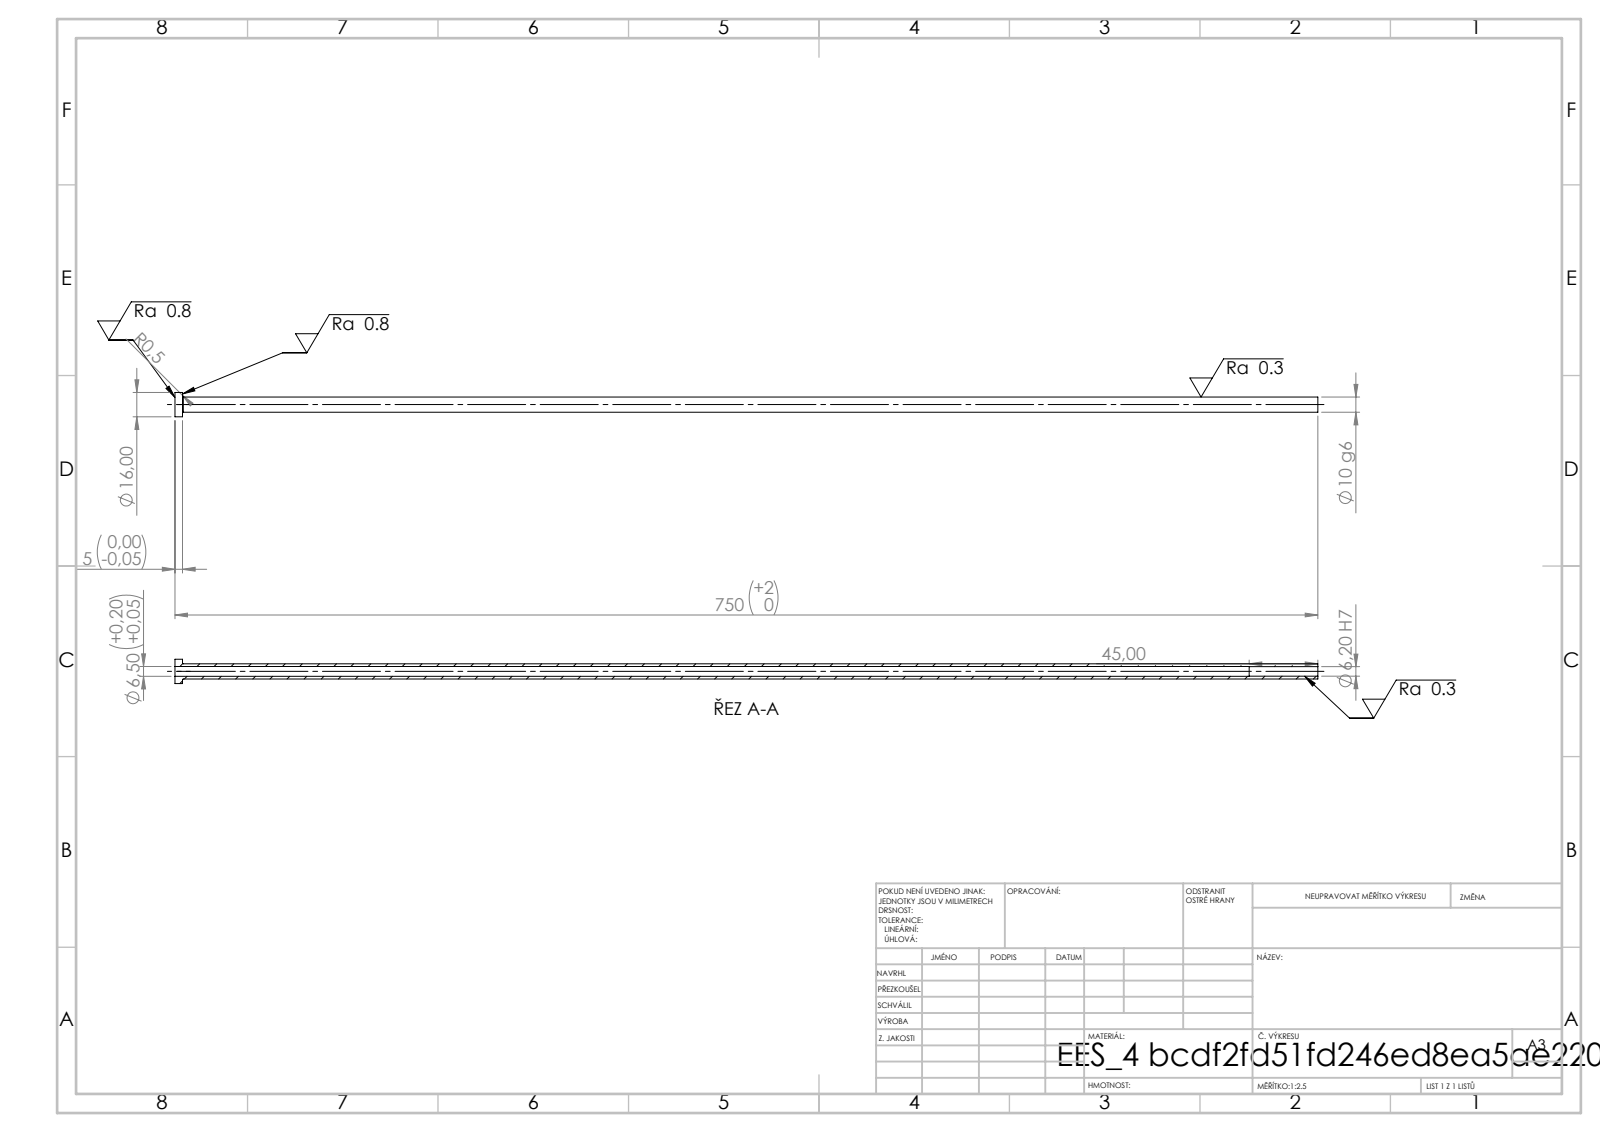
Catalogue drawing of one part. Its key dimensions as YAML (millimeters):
step_written_by: "SolidWorks 2019 (CONFIG_CONTROL_DESIGN)"
units: millimeters
bodies: {solids: 1, faces: 14, planar: 4, cylindrical: 8, other: 2}
overall_size: [750, 16, 16]
volume: 34767
surface_area: 39264
round_holes:
  - {diameter: 6.2, count: 1}
  - {diameter: 6.5, count: 1}
round_bosses_or_shafts:
  - {diameter: 16, count: 1}
  - {diameter: 10, count: 1}
face_to_face_distances: [5, 750, 745, 705, 700, 45]
